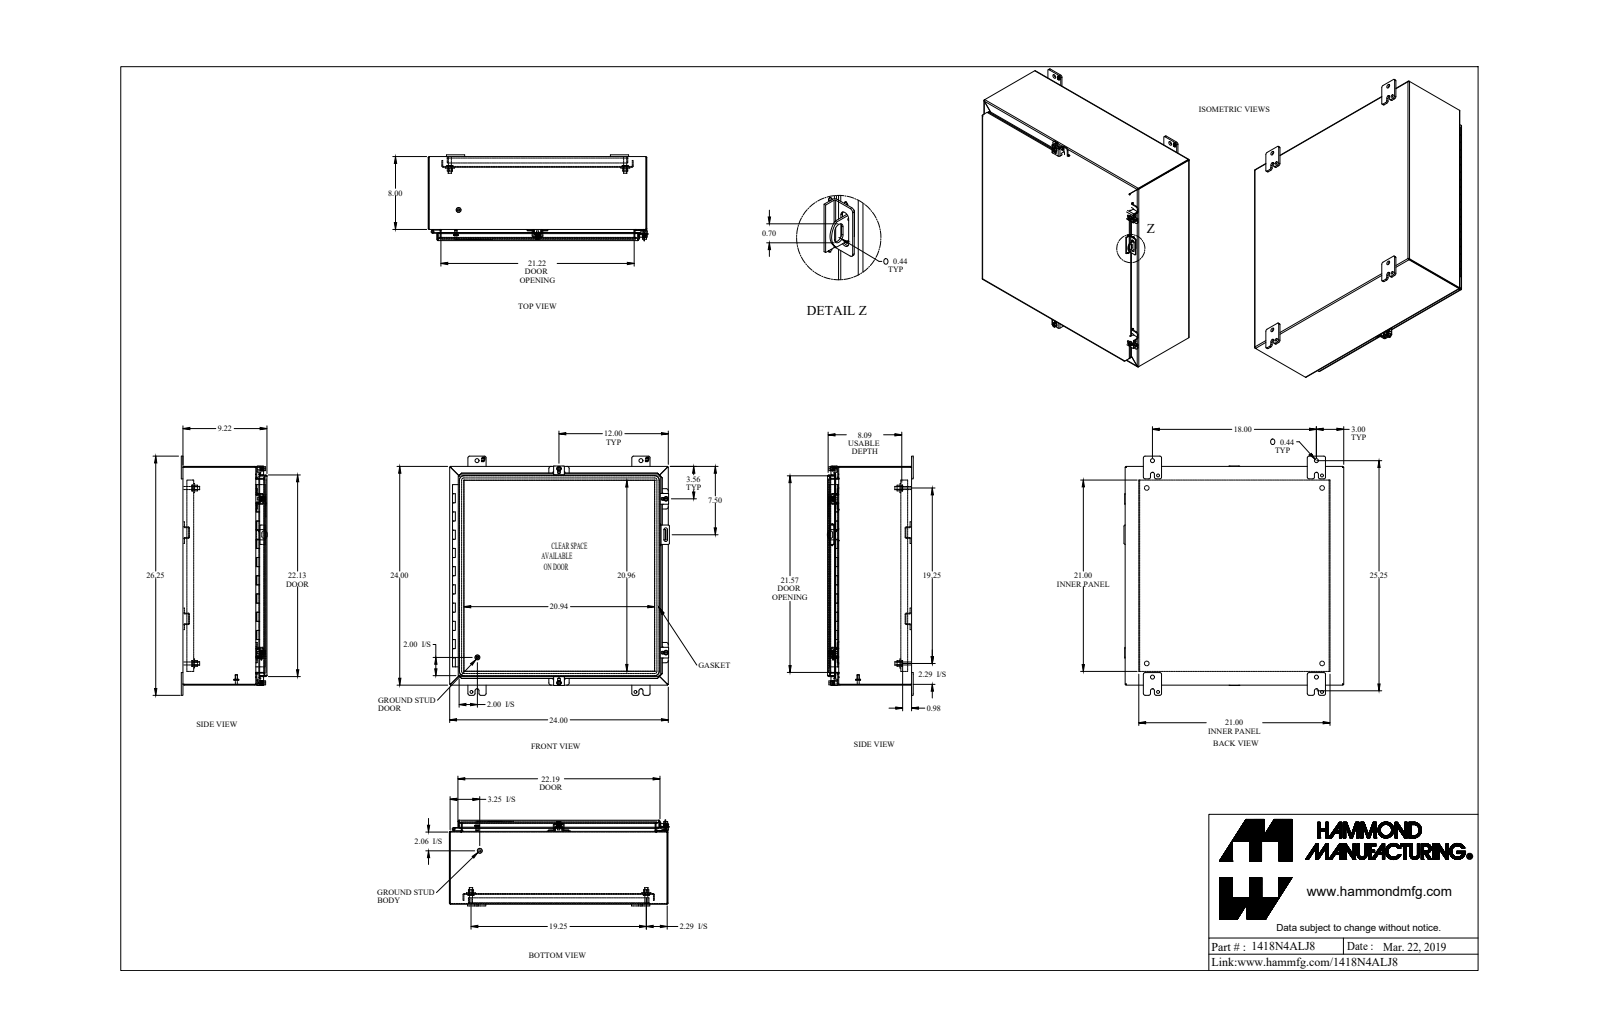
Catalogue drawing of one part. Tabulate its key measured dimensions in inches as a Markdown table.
| quantity | value |
| --- | --- |
| part name | 1418N4ALJ8_Default |
| STEP written by | SolidWorks 2019 (CONFIG_CONTROL_DESIGN) |
| units | inches |
| bodies | 40 solids, 1568 faces (927 planar, 531 cylindrical, 110 other) |
| overall size | 26.25 × 24.126 × 9.438 |
| volume | 254.1 in³ |
| surface area | 5 863 in² |
| round holes (diameter × count) | 0.232 × 4, 0.265 × 4, 0.313 × 4, 0.375 × 4, 0.437 × 4, 0.5 × 4, 0.307 × 2, 0.445 × 2, 0.125 × 1, 0.187 × 1 |
| round bosses / shafts (diameter × count) | 0.131 × 12, 0.65 × 4, 0.5 × 4, 0.4 × 4, 0.375 × 4, 0.33 × 4, 0.244 × 4, 1 × 2 |
| partial cylindrical surfaces (radius × count) | 0.188 × 24, 0.05 × 22, 0.15 × 22, 0.25 × 20, 0.041 × 16, 0.122 × 16, 0.125 × 11, 0.04 × 10 |
| main face-to-face distances | 0.081, 23.919, 0.1, 9.041, 9.122, 9.141, 9.222, 0.095, 8.046, 7.946 |
| hole center spacings | 9.857, 18, 19.25, 19.25, 27.223, 2.434, 18.187, 20.759 |
